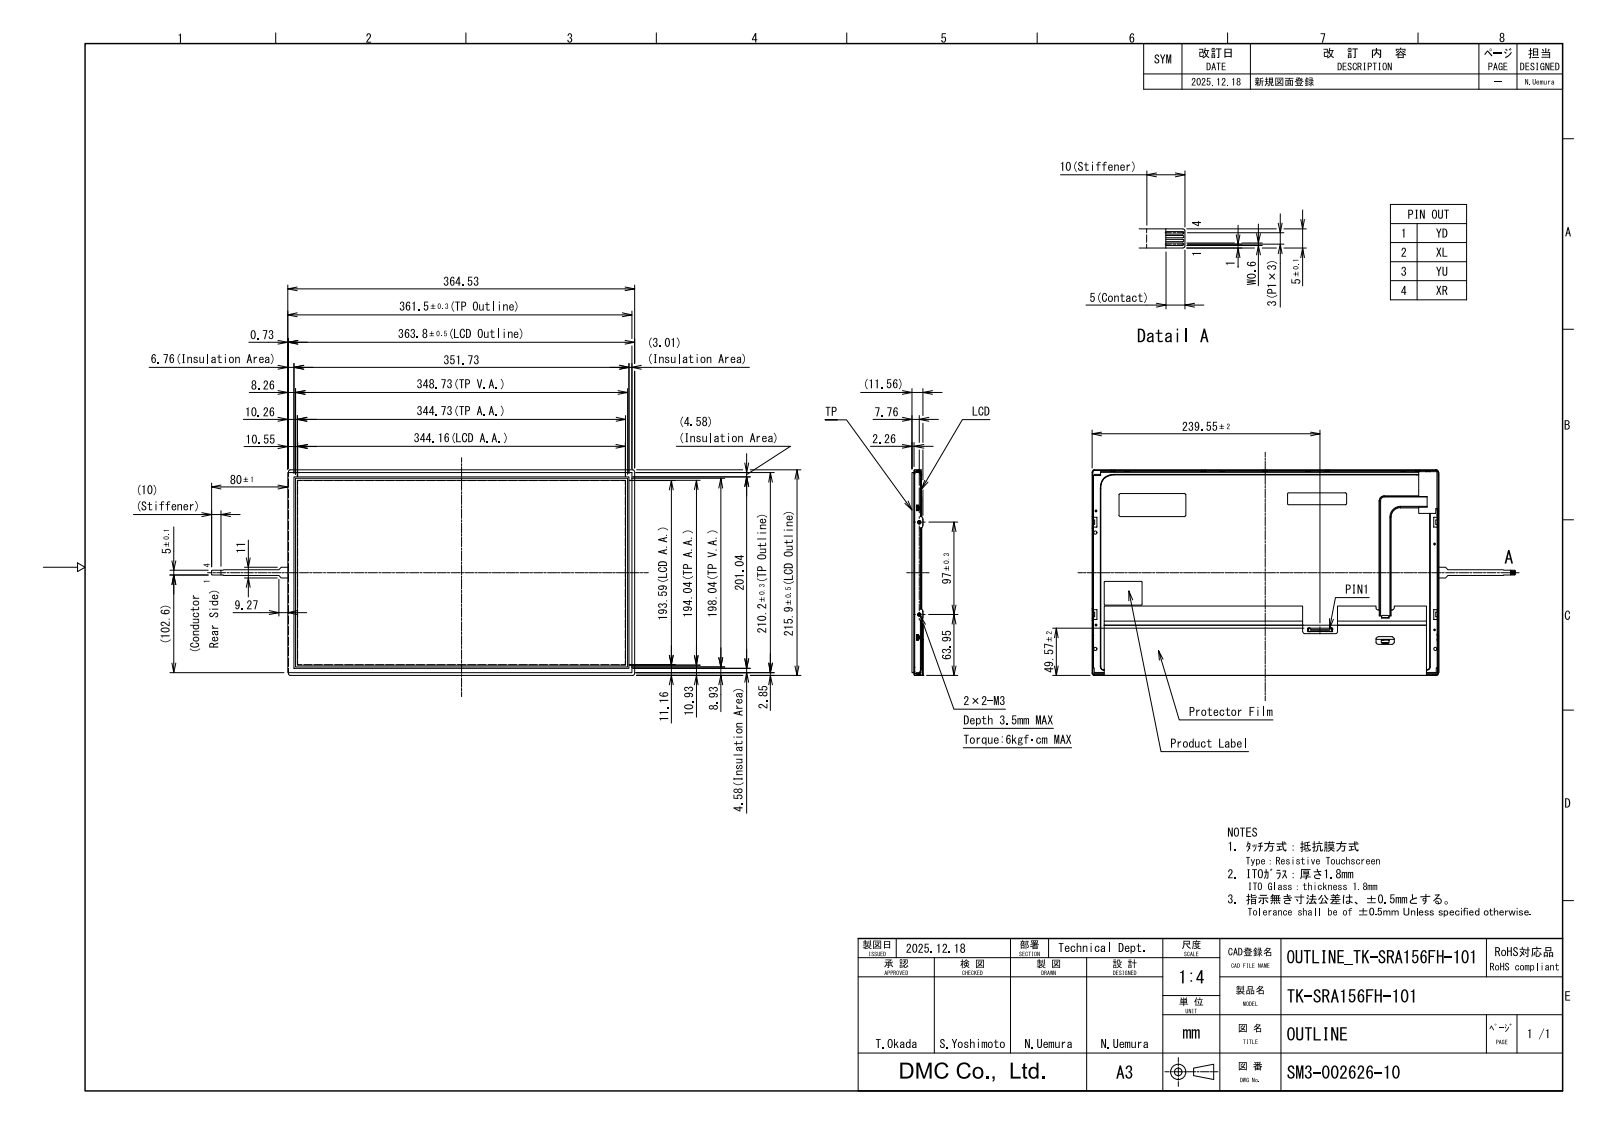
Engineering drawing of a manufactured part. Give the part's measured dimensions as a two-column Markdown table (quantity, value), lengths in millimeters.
| quantity | value |
| --- | --- |
| STEP written by | Autodesk Inventor 2024 (AUTOMOTIVE_DESIGN) |
| units | millimeters |
| bodies | 1 solid, 3674 faces (2150 planar, 1234 cylindrical, 290 other) |
| overall size | 444.52 × 216 × 11.56 |
| volume | 338 508 mm³ |
| surface area | 388 076 mm² |
| round holes (diameter × count) | 0.9 × 4, 3.05 × 4, 3.5 × 3, 3.8 × 3, 0.5 × 2, 2.5 × 2, 3 × 2, 4 × 2 |
| round bosses / shafts (diameter × count) | 2.5 × 4, 6 × 3, 1.97 × 3, 4.6 × 2 |
| partial cylindrical surfaces (radius × count) | 1 × 137, 0.3 × 130, 0.5 × 96, 0.1 × 70, 0.2 × 58, 0.8 × 44, 0.6 × 23, 0.7 × 20 |
| main face-to-face distances | 3.38, 5.03, 8.41, 0.8, 9.21, 5.83, 2.25, 0.9, 11.46, 2.35 |
| hole center spacings | 97, 9.3, 9.7, 20, 20.01, 20.73, 21.75, 23.01 |
